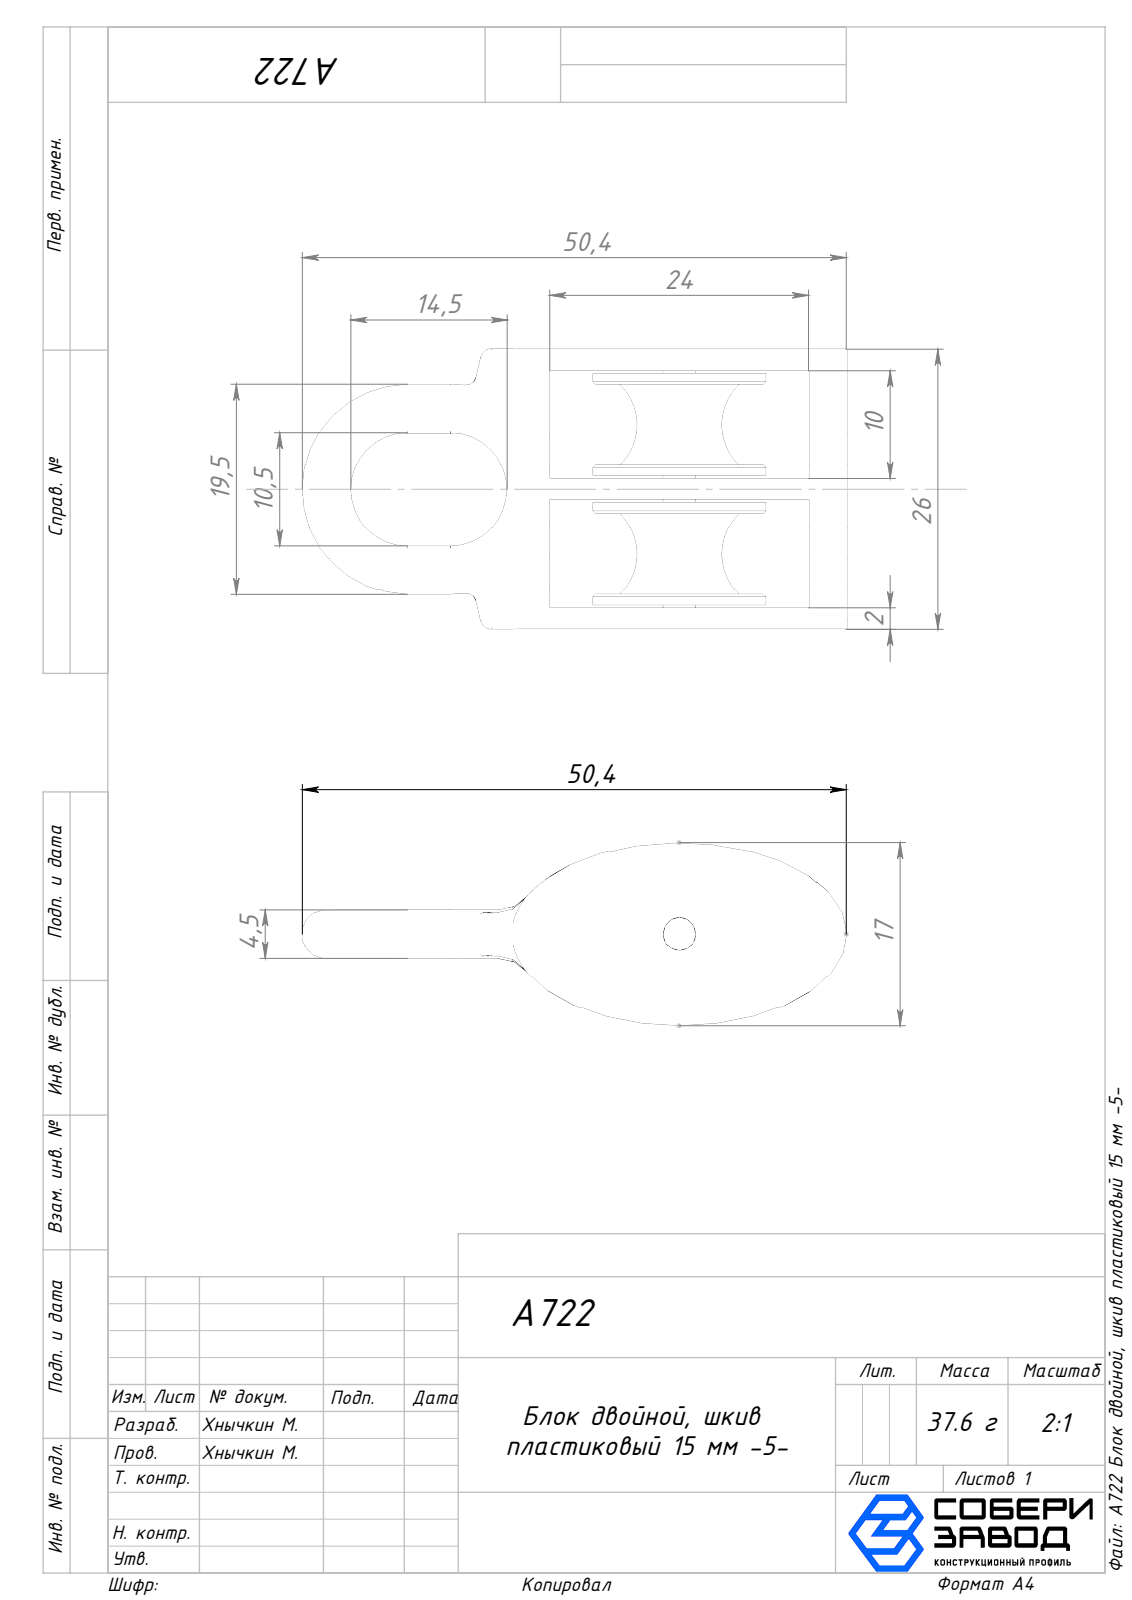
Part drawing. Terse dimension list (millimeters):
name: A722 Блок двойной, шкив пластиковый 15 мм -5; A722 Корпус_00; A722 Ролик_00; A722 Вал_00
written by: SolidWorks 2025 (AUTOMOTIVE_DESIGN)
unit: mm
bodies: 4 solids, 122 faces (26 planar, 38 cylindrical, 58 other)
size: 50.45 × 26 × 17
volume: 6 097 mm³; area: 6 615 mm²
holes: 1× ⌀3
bosses: 2× ⌀4.5, 1× ⌀16
rounds: 10× R1, 2× R3
face distances: 12, 2, 24, 2.25, 11.75, 9.75, 14, 10, 26, 14.25
